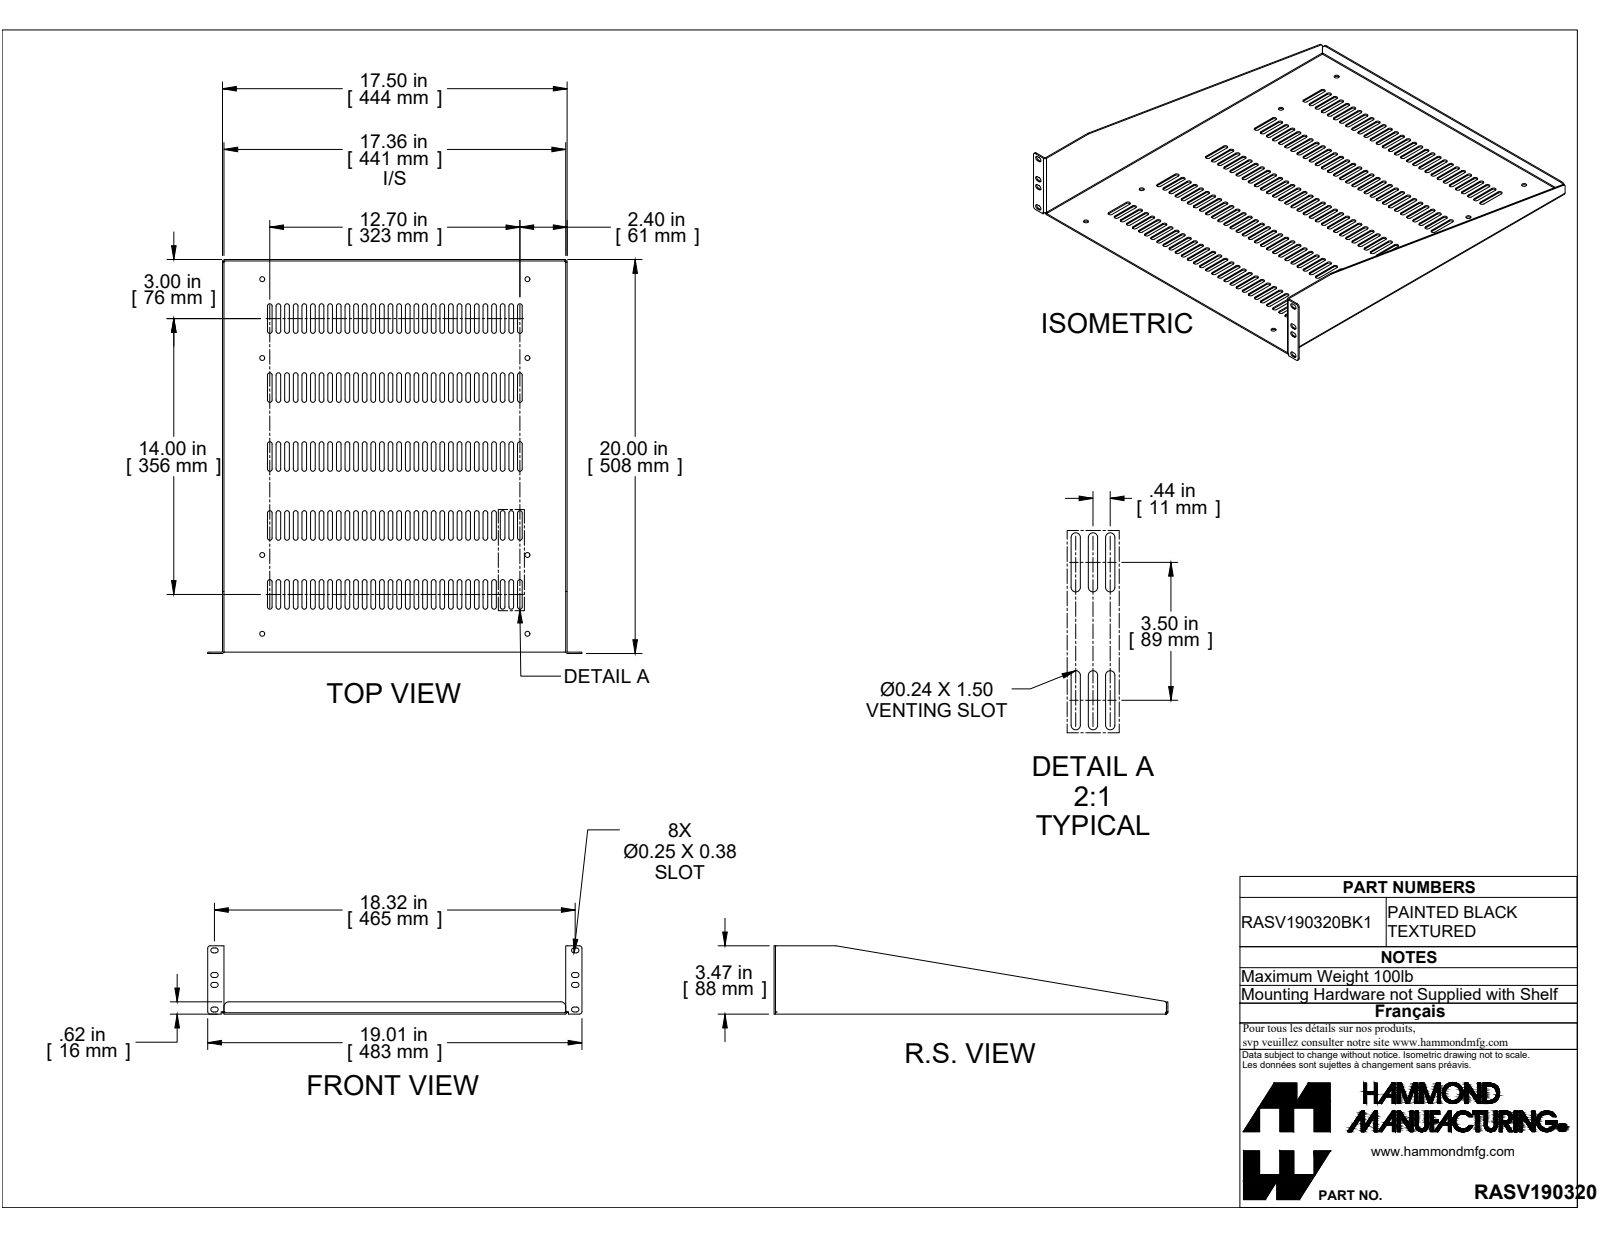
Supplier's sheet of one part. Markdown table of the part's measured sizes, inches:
| quantity | value |
| --- | --- |
| part name | RASV190320BK1 |
| STEP written by | SolidWorks 2019 (CONFIG_CONTROL_DESIGN) |
| units | inches |
| bodies | 1 solid, 704 faces (356 planar, 344 cylindrical, 4 other) |
| overall size | 20 × 19.006 × 3.468 |
| volume | 28.6 in³ |
| surface area | 837.1 in² |
| round holes (diameter × count) | 0.25 × 8 |
| partial cylindrical surfaces (radius × count) | 0.118 × 290, 0.125 × 20, 0.117 × 10, 0.036 × 5, 0.108 × 5, 0.055 × 3, 0.25 × 2 |
| main face-to-face distances | 0.072, 17.428, 17.356, 17.5, 19.856, 19.928, 0.876, 0.072, 19.928, 20 |
| hole center spacings | 4, 13.468, 14, 14.049, 19.426, 10, 16.774, 18 |
